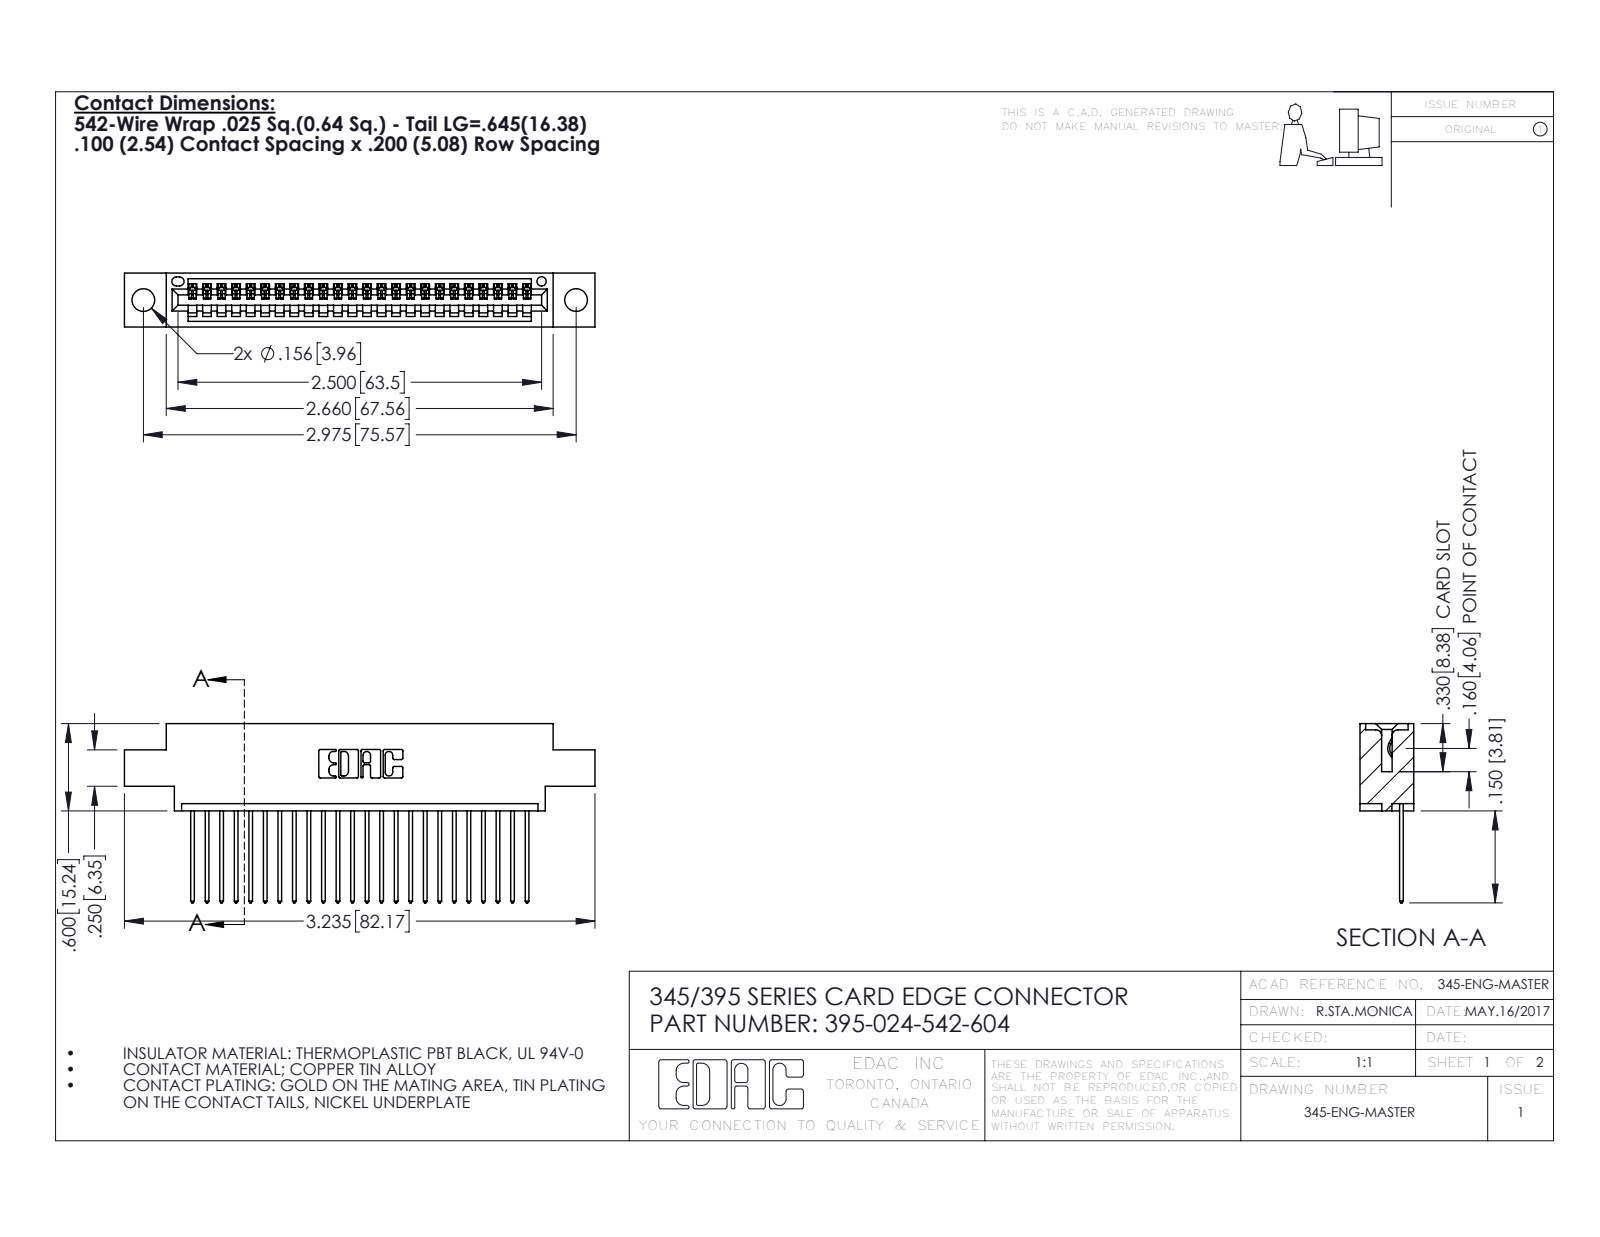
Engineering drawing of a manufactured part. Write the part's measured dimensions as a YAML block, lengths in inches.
part_name: "345 Part_0.170 Offset - 0.156 Dia-TH; 345-292-001_345-293-142; 395-024-542-604"
step_written_by: "SolidWorks 2016 (CONFIG_CONTROL_DESIGN)"
units: inches
bodies: {solids: 25, faces: 1522, planar: 1044, cylindrical: 478, other: 0}
overall_size: [3.235, 1.232, 0.37]
volume: 0.458
surface_area: 15.51
round_holes:
  - {diameter: 0.156, count: 2}
  - {diameter: 0.064, count: 1}
partial_cylinders:
  - {radius: 0.006, count: 48}
  - {radius: 0.01, count: 48}
  - {radius: 0.01, count: 22}
  - {radius: 0.007, count: 6}
  - {radius: 0.031, count: 6}
  - {radius: 0.026, count: 3}
  - {radius: 0.031, count: 2}
  - {radius: 0.04, count: 2}
face_to_face_distances: [0.298, 0.072, 0.37, 0.2, 0.098, 0.272, 0.025, 0.225, 0.175, 0.149]
hole_center_spacings: [0.27, 2.741, 2.975]
